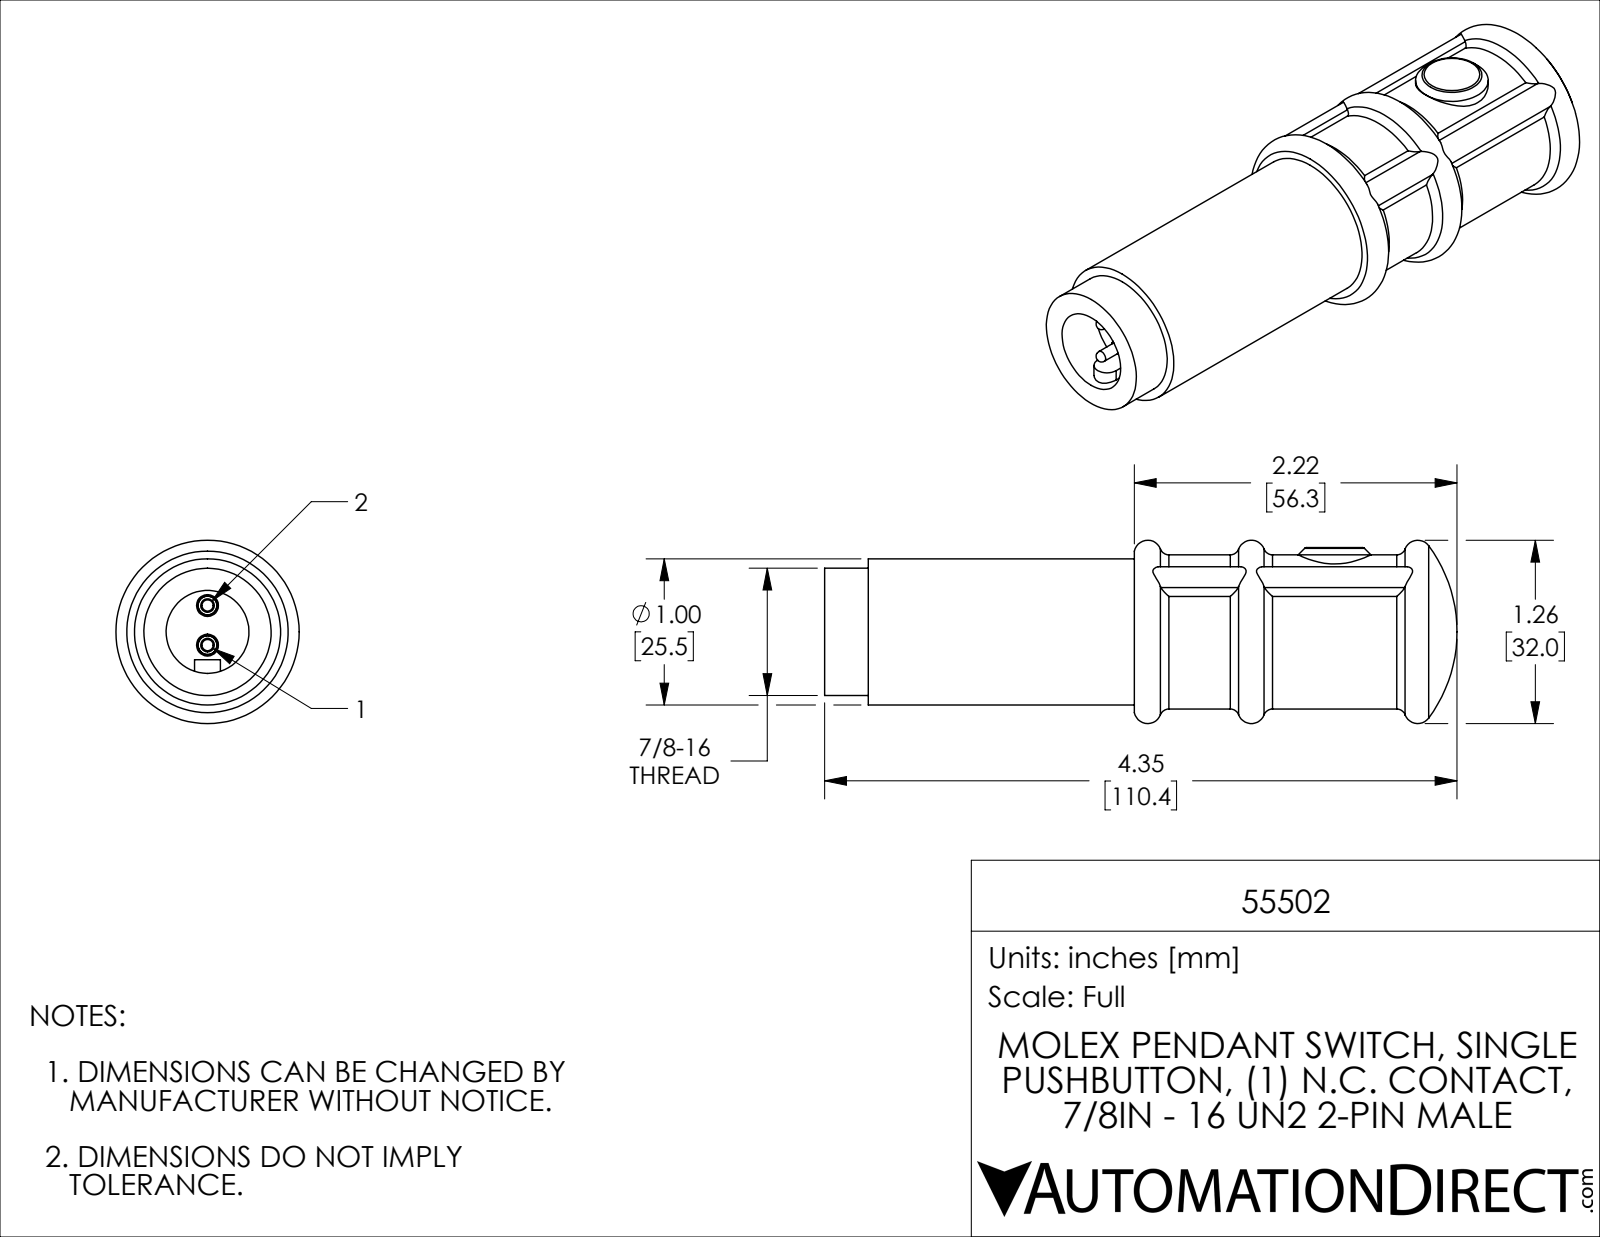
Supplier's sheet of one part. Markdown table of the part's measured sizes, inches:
| quantity | value |
| --- | --- |
| part name | 55502 |
| STEP written by | SolidWorks 2021 (CONFIG_CONTROL_DESIGN) |
| units | inches |
| bodies | 3 solids, 88 faces (12 planar, 38 cylindrical, 38 other) |
| overall size | 4.348 × 1.26 × 1.26 |
| volume | 3.659 in³ |
| surface area | 18.01 in² |
| round holes (diameter × count) | 0.57 × 1 |
| round bosses / shafts (diameter × count) | 0.077 × 2, 1.059 × 1, 1.005 × 1, 0.875 × 1, 0.5 × 1 |
| partial cylindrical surfaces (radius × count) | 0.062 × 4, 0.094 × 3, 0.089 × 1, 0.529 × 1 |
| main face-to-face distances | 0.333, 0.3, 0.033, 2.13, 1.83, 1.797, 0.771, 0.178, 0.243, 0.057 |
